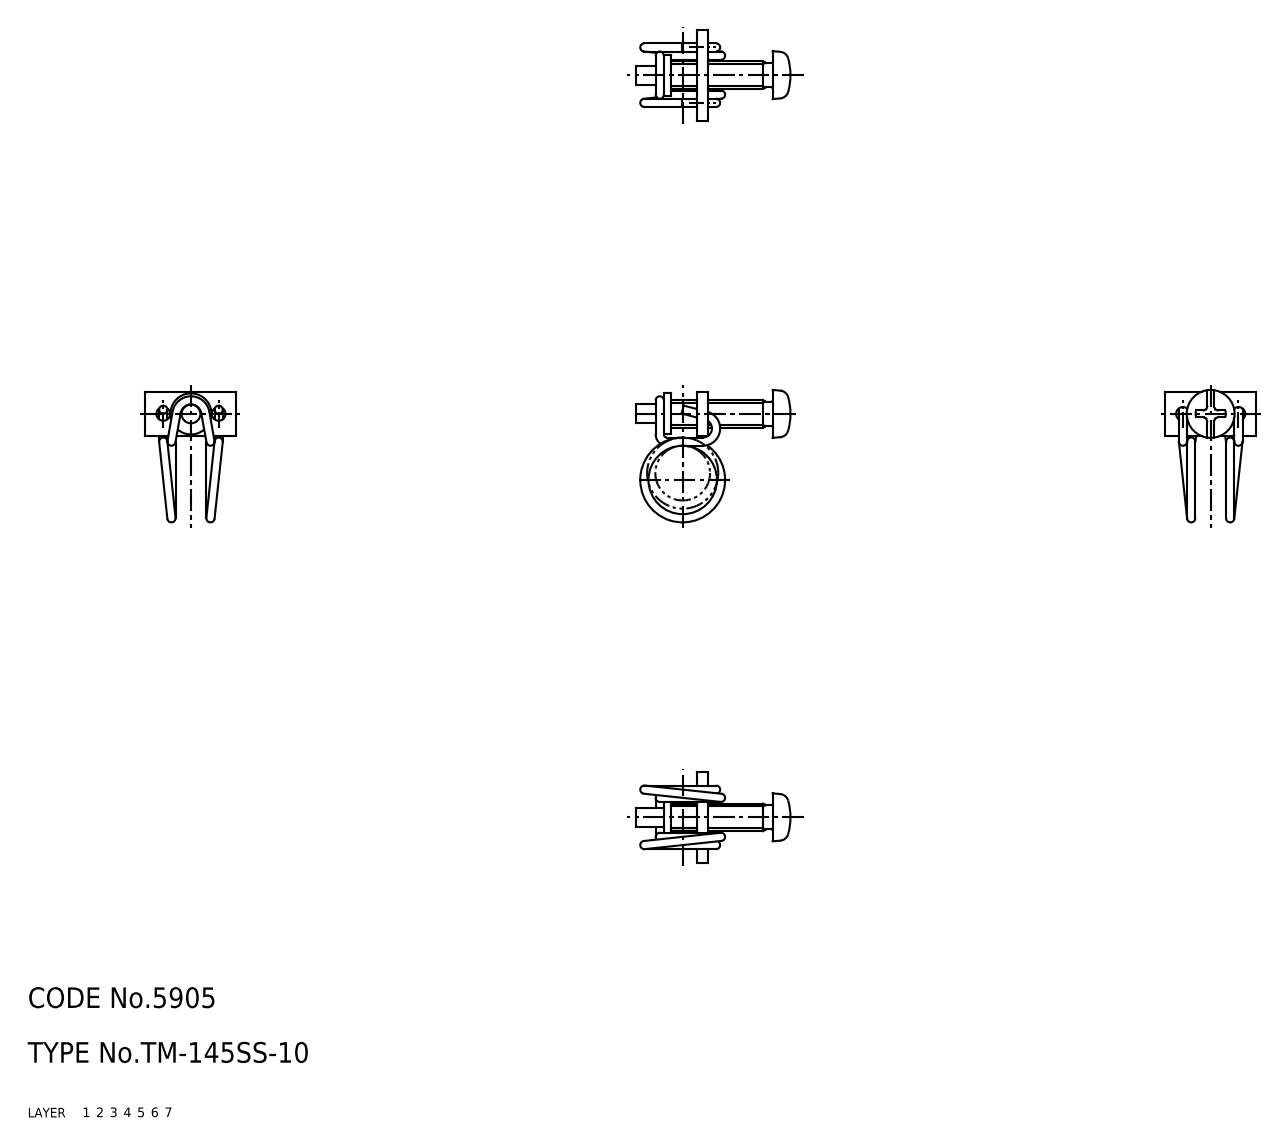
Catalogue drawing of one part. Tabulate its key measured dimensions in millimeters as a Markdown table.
| quantity | value |
| --- | --- |
| part name | 67115636; 67115649; 67115662 |
| STEP written by | CADfix (AUTOMOTIVE_DESIGN) |
| units | millimeters |
| bodies | 3 solids, 75 faces (0 planar, 0 cylindrical, 75 other) |
| overall size | 22.57 × 19.35 × 13.3 |
| volume | 545 mm³ |
| surface area | 1 082 mm² |
